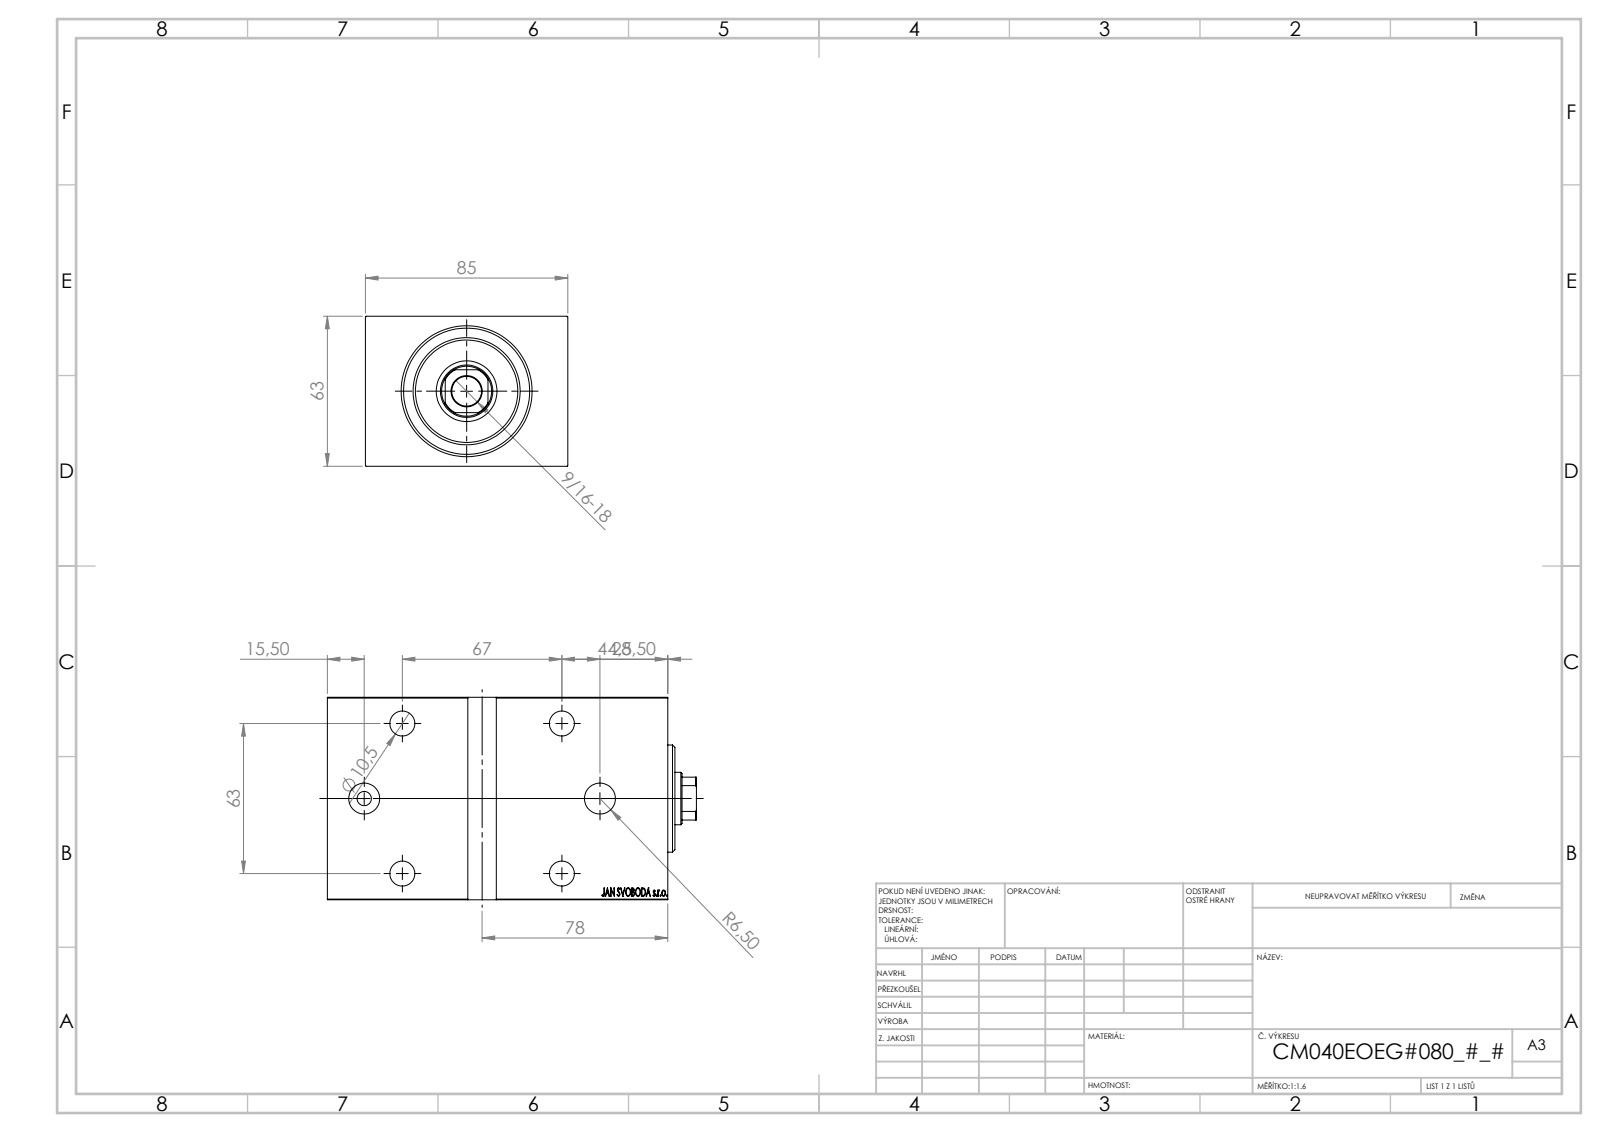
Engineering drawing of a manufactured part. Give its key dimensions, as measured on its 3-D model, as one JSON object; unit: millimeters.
{"part_name": "V450CM_E_VCP; V450CM_E_Body; V450CM_VC_B", "step_written_by": "SolidWorks 2019 (CONFIG_CONTROL_DESIGN)", "units": "millimeters", "bodies": {"solids": 3, "faces": 849, "planar": 409, "cylindrical": 46, "other": 394}, "overall_size": [155, 85, 63], "volume_mm3": 672240, "surface_area_mm2": 102127, "round_holes": [[10.5, 4], [16.5, 4], [13, 2], [12.5, 1], [22, 1], [25.5, 1], [40, 1], [53, 1]], "round_bosses_or_shafts": [[45, 1], [42, 1], [6, 1]], "partial_cylinders_radius": [[10.5, 1]], "face_to_face_distances": [63, 85, 143, 12, 131, 3, 5, 138, 126, 8], "hole_center_spacings": [35.33, 88.78, 63, 67, 91.97, 99]}
